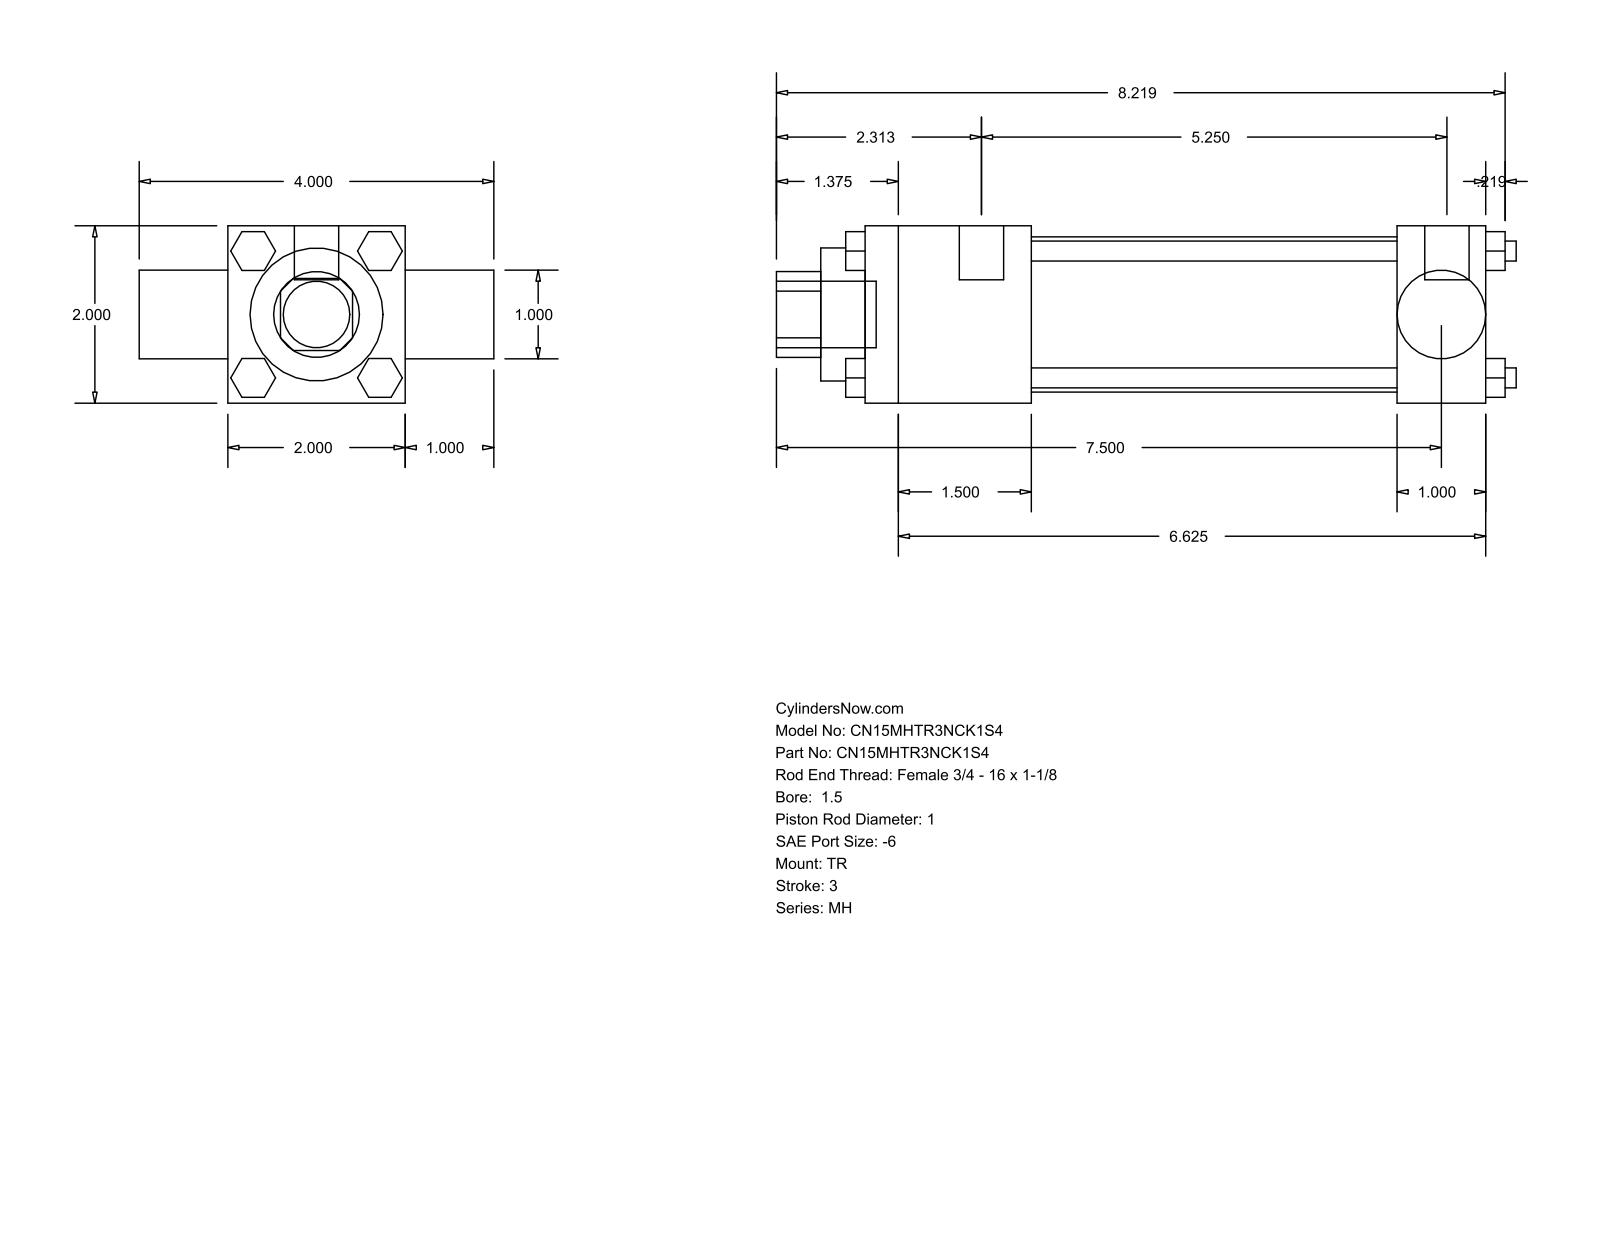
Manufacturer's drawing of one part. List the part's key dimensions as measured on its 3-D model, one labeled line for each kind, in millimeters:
Part name (STEP PRODUCT): MH_TR__0150_1
STEP written by: GSSL Pune (CONFIG_CONTROL_DESIGN)
Units: millimetres
Bodies: 0 solids, 120 faces (92 planar, 28 cylindrical, 0 other)
Overall size (bounding box): 211.93 × 101.6 × 50.8
Round holes (diameter × count): ⌀25.35 ×1, ⌀25.4 ×1, ⌀38.1 ×1, ⌀44.45 ×1
Round bosses / shafts (diameter × count): ⌀5.71 ×4, ⌀5.56 ×3, ⌀12.7 ×2, ⌀19.05 ×1
Partial cylindrical surfaces — rounded edges, fillets, slot ends (radius × count): R12.29 ×1
Main face-to-face distances: 50.8, 25.4, 177.8, 76.2, 47.63, 130.17, 152.4, 104.77, 183.36, 12.7
